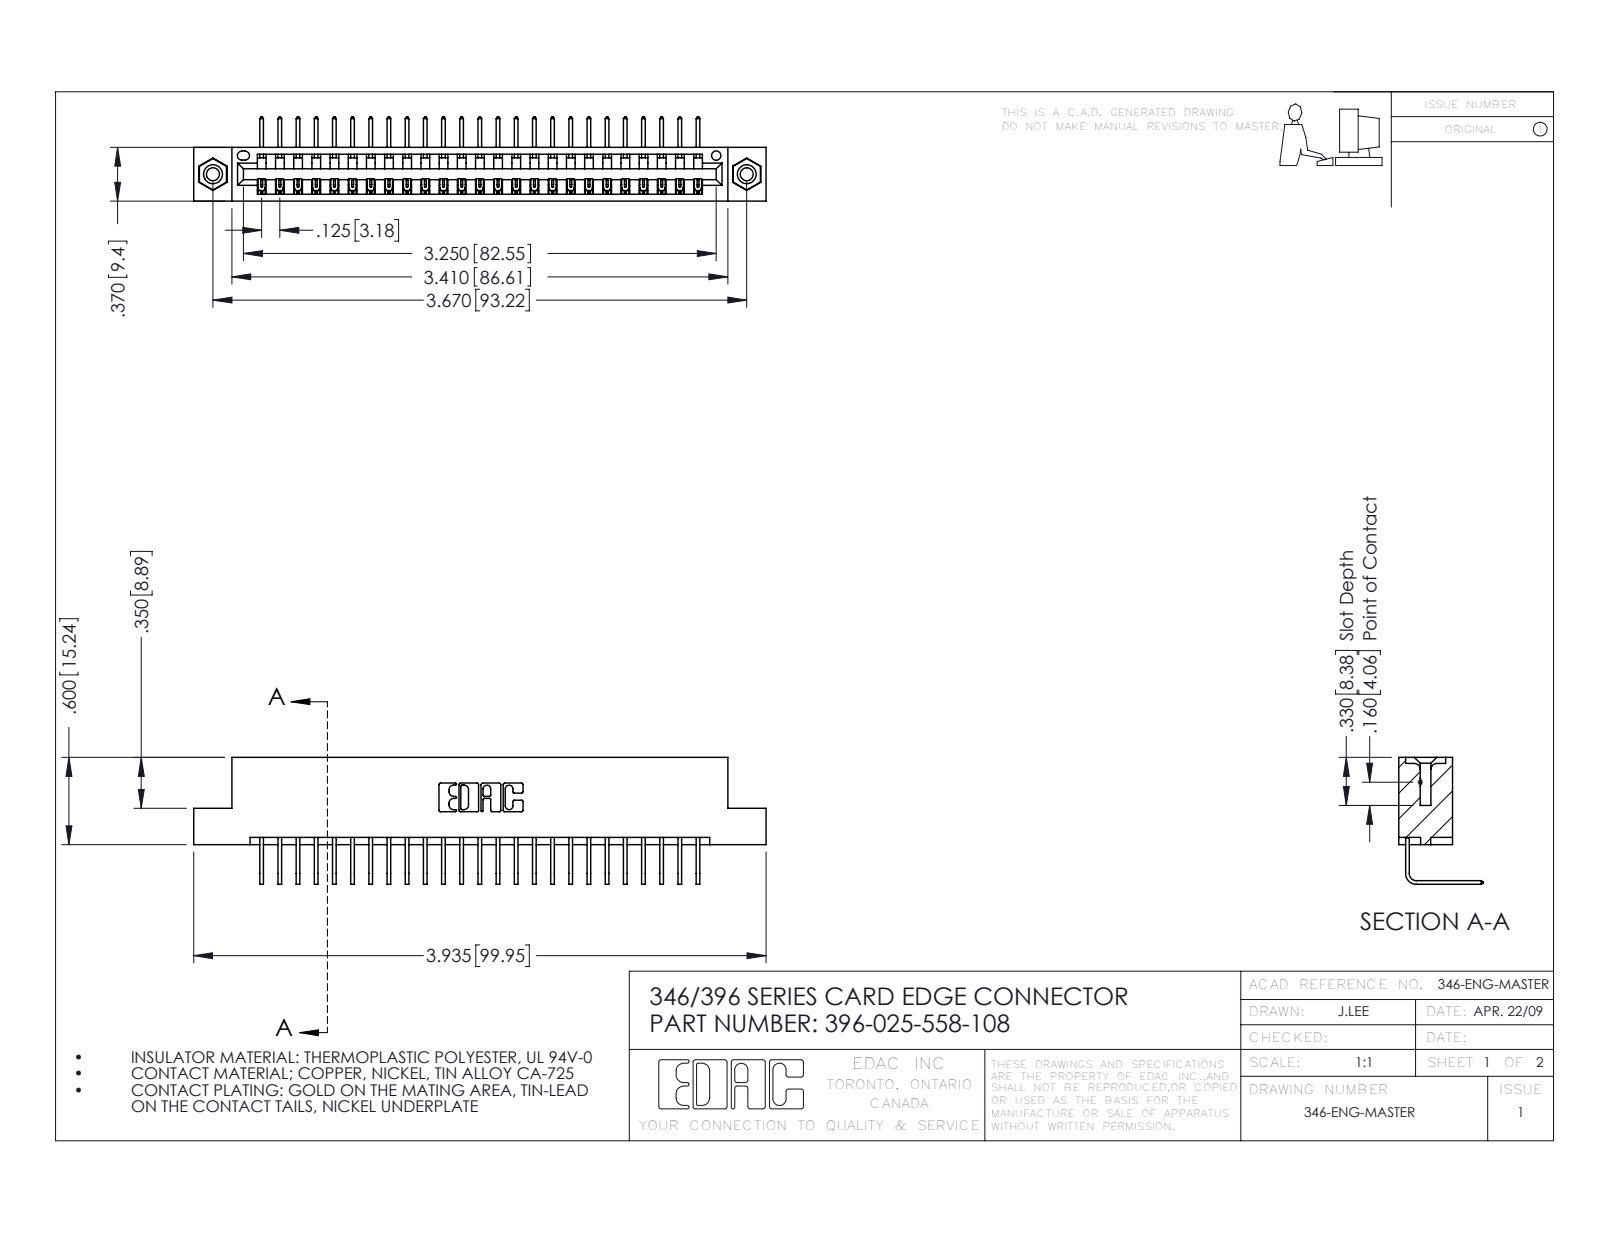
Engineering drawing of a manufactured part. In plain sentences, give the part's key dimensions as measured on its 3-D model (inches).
The part is named "396-025-558-108; 345-250-001_345-250-003-102; 345-292-001_558 Tail - 2; 346 Part_Flush Mounting Lugs - 0.156 Dia-TI". Its 3-D file was written by "SolidWorks 2016 (CONFIG_CONTROL_DESIGN)". It is 28 solids with 1682 faces: 1158 planar, 508 cylindrical and 16 other. Overall it measures 3.935 by 0.873 by 0.58 inches. Its volume is 0.581 cubic inches and its surface area 18.98 square inches. Round holes: 2 of diameter 0.089, 2 of diameter 0.125, 2 of diameter 0.156, 1 of diameter 0.064. Round bosses or shafts: 2 of diameter 0.155. Partial cylindrical surfaces (rounded edges, fillets, slot ends): 50 of radius 0.006, 22 of radius 0.01, 6 of radius 0.007, 6 of radius 0.031, 3 of radius 0.026, 2 of radius 0.031, 2 of radius 0.04, 1 of radius 0.014. The main face-to-face distances are 0.322, 0.048, 0.37, 0.25, 0.298, 0.025, 0.072, 0.148, 0.222, 0.1. The hole center spacings are 0.246, 3.462, 3.67.
